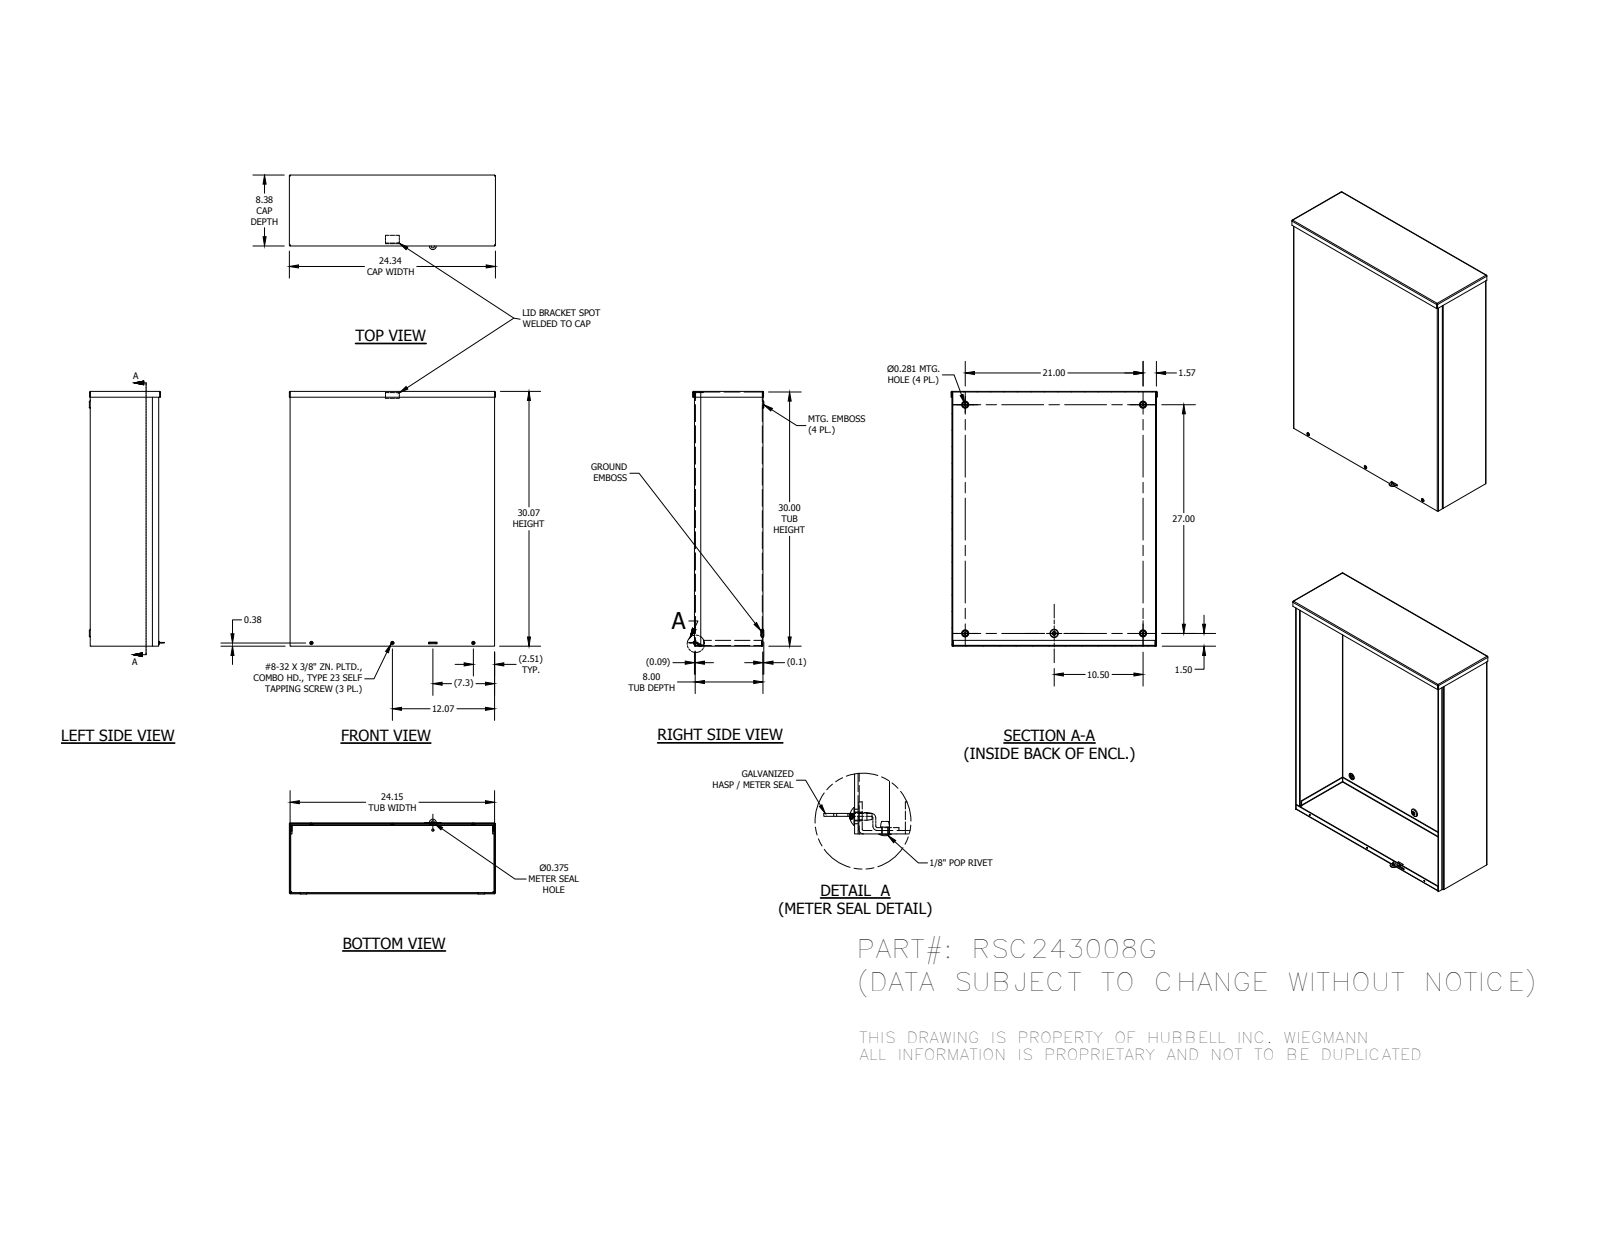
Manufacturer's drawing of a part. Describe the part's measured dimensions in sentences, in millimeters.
The part is named "RSC243008GBKPA; RSC2408GEWPA; RSC2430GLFA; RSC2408GCPA (+5 more)". Its 3-D file was written by "Autodesk Inventor 2014 (AUTOMOTIVE_DESIGN)". It is 10 solids with 350 faces: 193 planar, 66 cylindrical and 91 other. Overall it measures 764.9 by 618.12 by 224.8 millimeters. Its volume is 2 953 000 cubic millimeters and its surface area 3 163 000 square millimeters. Round holes: 6 of diameter 7.94, 4 of diameter 7.14, 3 of diameter 3.73, 1 of diameter 3.17, 1 of diameter 3.45, 1 of diameter 4.34, 1 of diameter 9.52. Round bosses or shafts: 3 of diameter 9.75, 3 of diameter 4.17, 1 of diameter 6.65, 1 of diameter 5.93, 1 of diameter 3.17. Partial cylindrical surfaces (rounded edges, fillets, slot ends): 19 of radius 0.79, 17 of radius 2.67, 2 of radius 2.37, 1 of radius 10.16. The main face-to-face distances are 1.88, 203.6, 205.48, 201.72, 611.48, 762, 609.6, 613.36, 763.88, 760.12. The hole center spacings are 242.89, 268.23, 510.39, 762.54, 781.65, 37.2, 485.78, 714.78.
